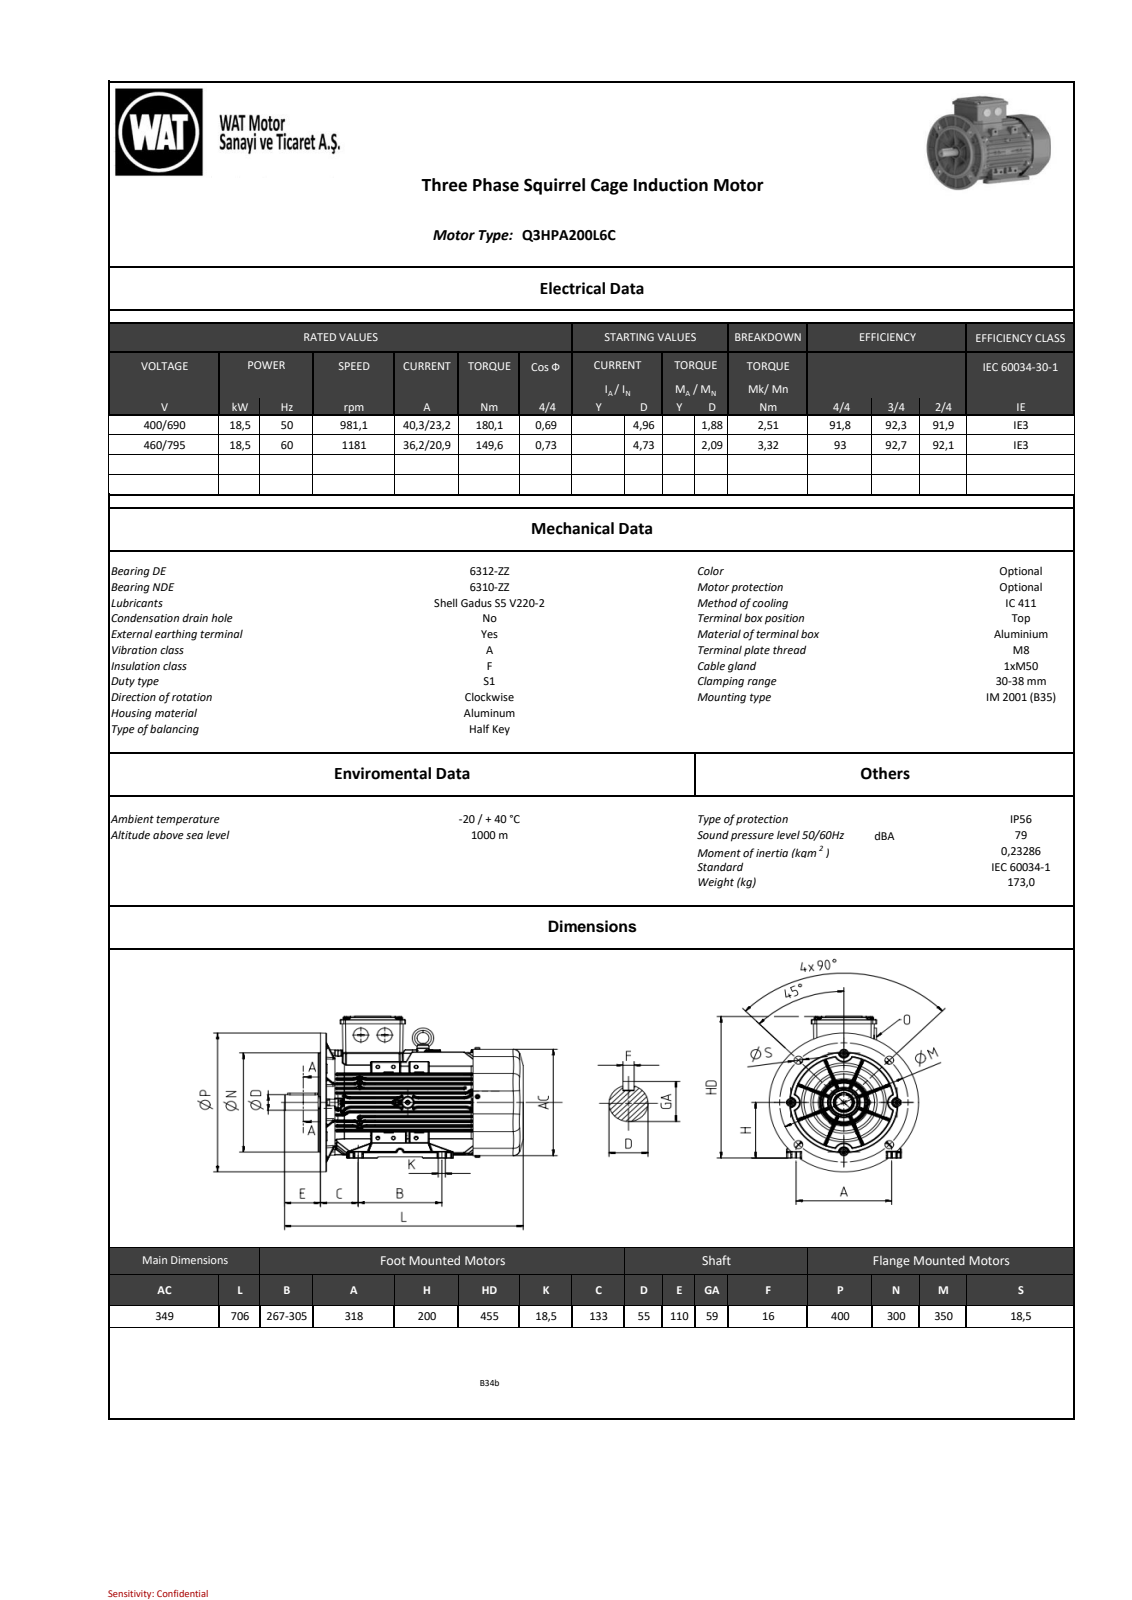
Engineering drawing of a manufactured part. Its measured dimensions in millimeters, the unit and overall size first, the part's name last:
Units: millimetres
Overall size (bounding box): 705.5 × 452 × 399.69
Round holes (diameter × count): ⌀5.6 ×8, ⌀0.4 ×4, ⌀4.3 ×4, ⌀6.5 ×4, ⌀8.3 ×4, ⌀9 ×4, ⌀10.45 ×4, ⌀18.5 ×4, ⌀4 ×3, ⌀5.5 ×3, ⌀3.2 ×2, ⌀9.44 ×2
Round bosses / shafts (diameter × count): ⌀12 ×8, ⌀5.49 ×8, ⌀4.92 ×8, ⌀10 ×6, ⌀16 ×5, ⌀8 ×5, ⌀18.1 ×4, ⌀14.8 ×4
Partial cylindrical surfaces — rounded edges, fillets, slot ends (radius × count): R0.5 ×1736, R1 ×912, R2 ×908, R5 ×293, R1.5 ×172, R0.1 ×122, R0.75 ×99, R4 ×72
Main face-to-face distances: 1.2, 6, 16.21, 32.48, 16.27, 3, 171.05, 173.83, 141.35, 157.62
Hole centre spacings: 129.23, 310.46, 136, 78.16, 169.96, 156, 161, 174.99
Bodies: 0 solids, 15241 faces (3980 planar, 5934 cylindrical, 5327 other)
Part name (STEP PRODUCT): model1_objects
STEP written by: SIEMENS PLM Software NX2206.8101 (AUTOMOTIVE_DESIGN)
